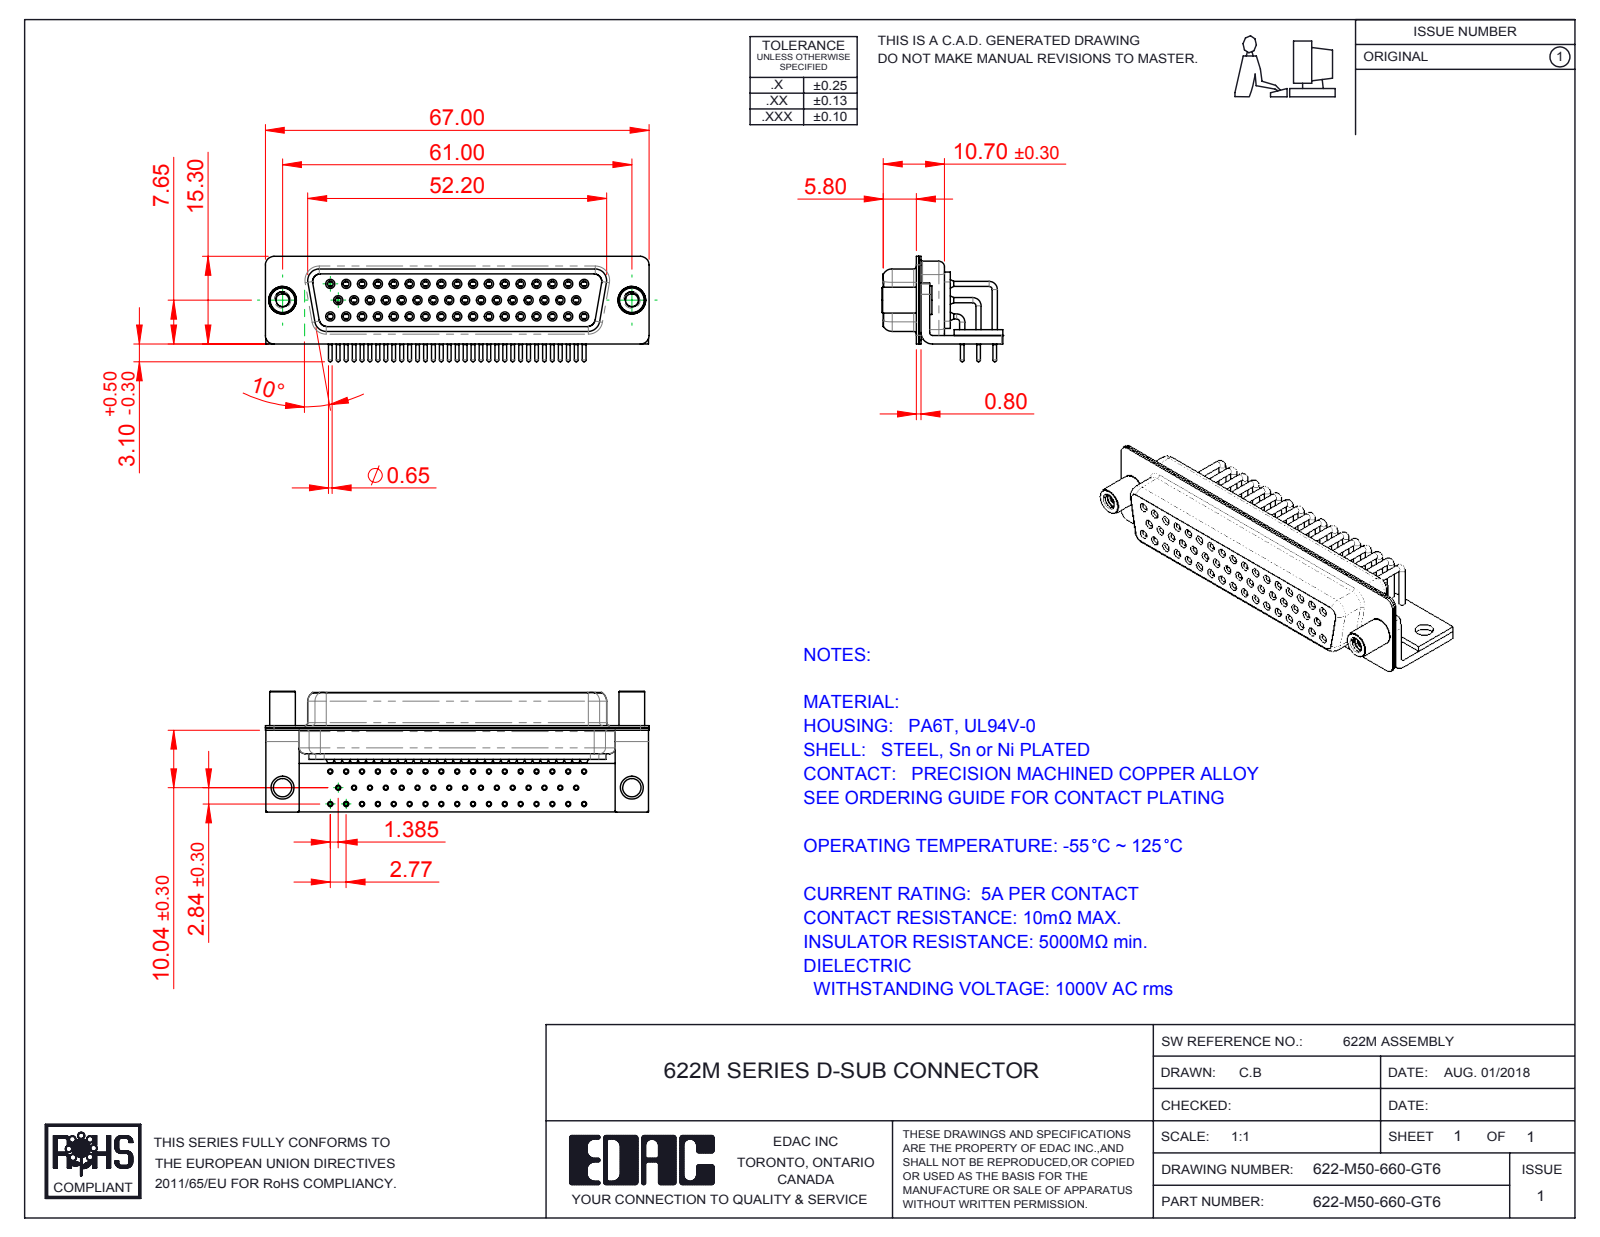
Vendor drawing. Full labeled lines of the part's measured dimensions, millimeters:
Part name (STEP PRODUCT): 622M Stabilizer Bracket_50 Contacts; 622M Housing_50 Contacts; 622-M50-660-GT6; 622M Contact Row 2_50 Contacts (+6 more)
STEP written by: SolidWorks 2016 (CONFIG_CONTROL_DESIGN)
Units: millimetres
Bodies: 58 solids, 3129 faces (845 planar, 1451 cylindrical, 833 other)
Overall size (bounding box): 67 × 21.1 × 18.4
Volume: 7 871 mm³ · Surface area: 18 434 mm²
Round holes (diameter × count): ⌀0.9 ×50, ⌀1 ×50, ⌀1.1 ×50, ⌀1.7 ×50, ⌀1.8 ×50, ⌀2 ×50, ⌀2.26 ×2, ⌀3.2 ×2, ⌀4 ×2, ⌀4.8 ×2
Round bosses / shafts (diameter × count): ⌀0.9 ×59, ⌀1.6 ×50, ⌀1.5 ×50, ⌀0.65 ×50, ⌀5 ×2, ⌀4.9 ×2, ⌀4.5 ×2
Partial cylindrical surfaces — rounded edges, fillets, slot ends (radius × count): R0.25 ×16, R1.5 ×16, R2 ×13, R1.35 ×8, R1.6 ×8, R0.5 ×5, R0.6 ×4, R0.65 ×4
Main face-to-face distances: 0.4, 1, 2.2, 0.85, 1.35, 11.85, 12.25, 5.8, 0.8, 5.9
Hole centre spacings: 2.77, 3.16, 5.54, 8.31, 11.08, 13.85, 16.62, 19.39
